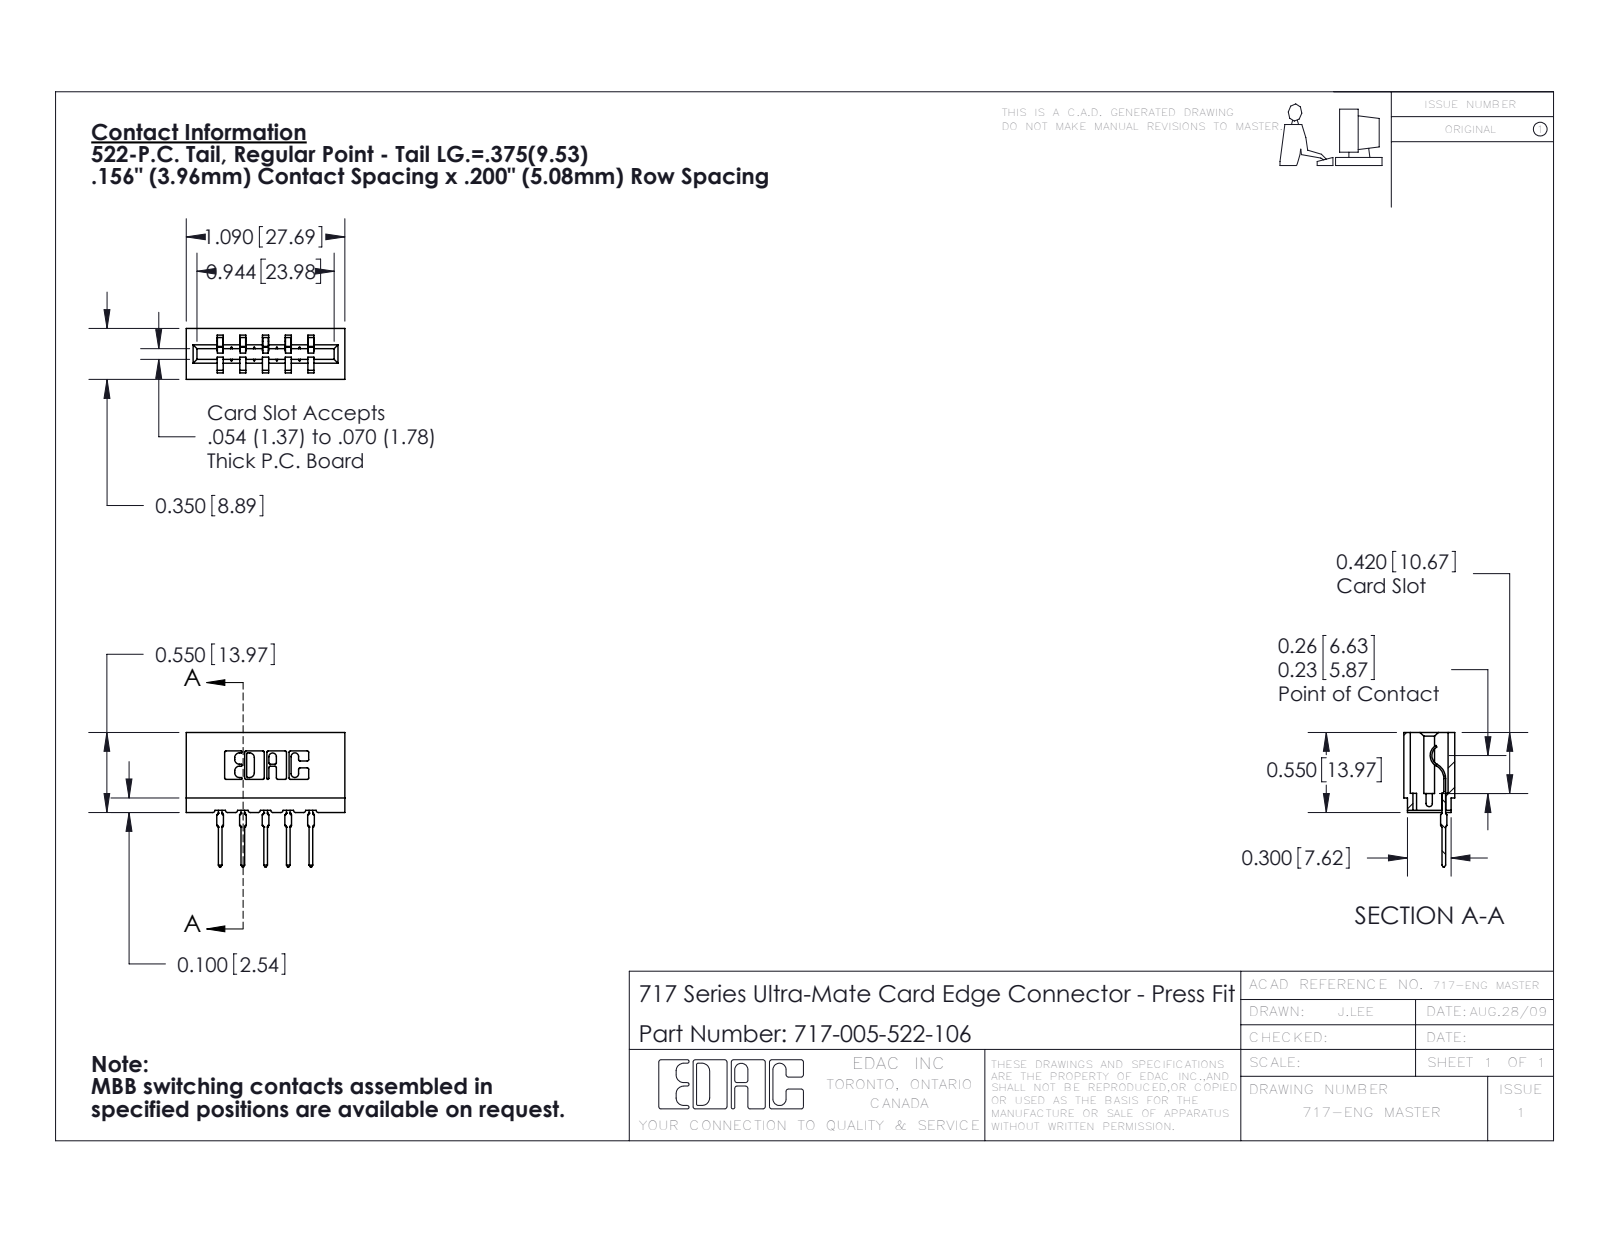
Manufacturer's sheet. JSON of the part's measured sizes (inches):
{"part_name": "717-005-522-106; 745-292-001_522; 717 Part_Insulator Option - 06", "step_written_by": "SolidWorks 2016 (CONFIG_CONTROL_DESIGN)", "units": "inches", "bodies": {"solids": 6, "faces": 659, "planar": 394, "cylindrical": 135, "other": 130}, "overall_size": [1.09, 0.924, 0.35], "volume_in3": 0.153, "surface_area_in2": 4.855, "partial_cylinders_radius": [[0.01, 22], [0.015, 10], [0.021, 10], [0.007, 6], [0.031, 6], [0.005, 4], [0.011, 4], [0.026, 3]], "face_to_face_distances": [0.212, 0.156, 0.138, 0.35, 0.198, 0.042, 0.312, 0.312, 0.468, 0.074]}
